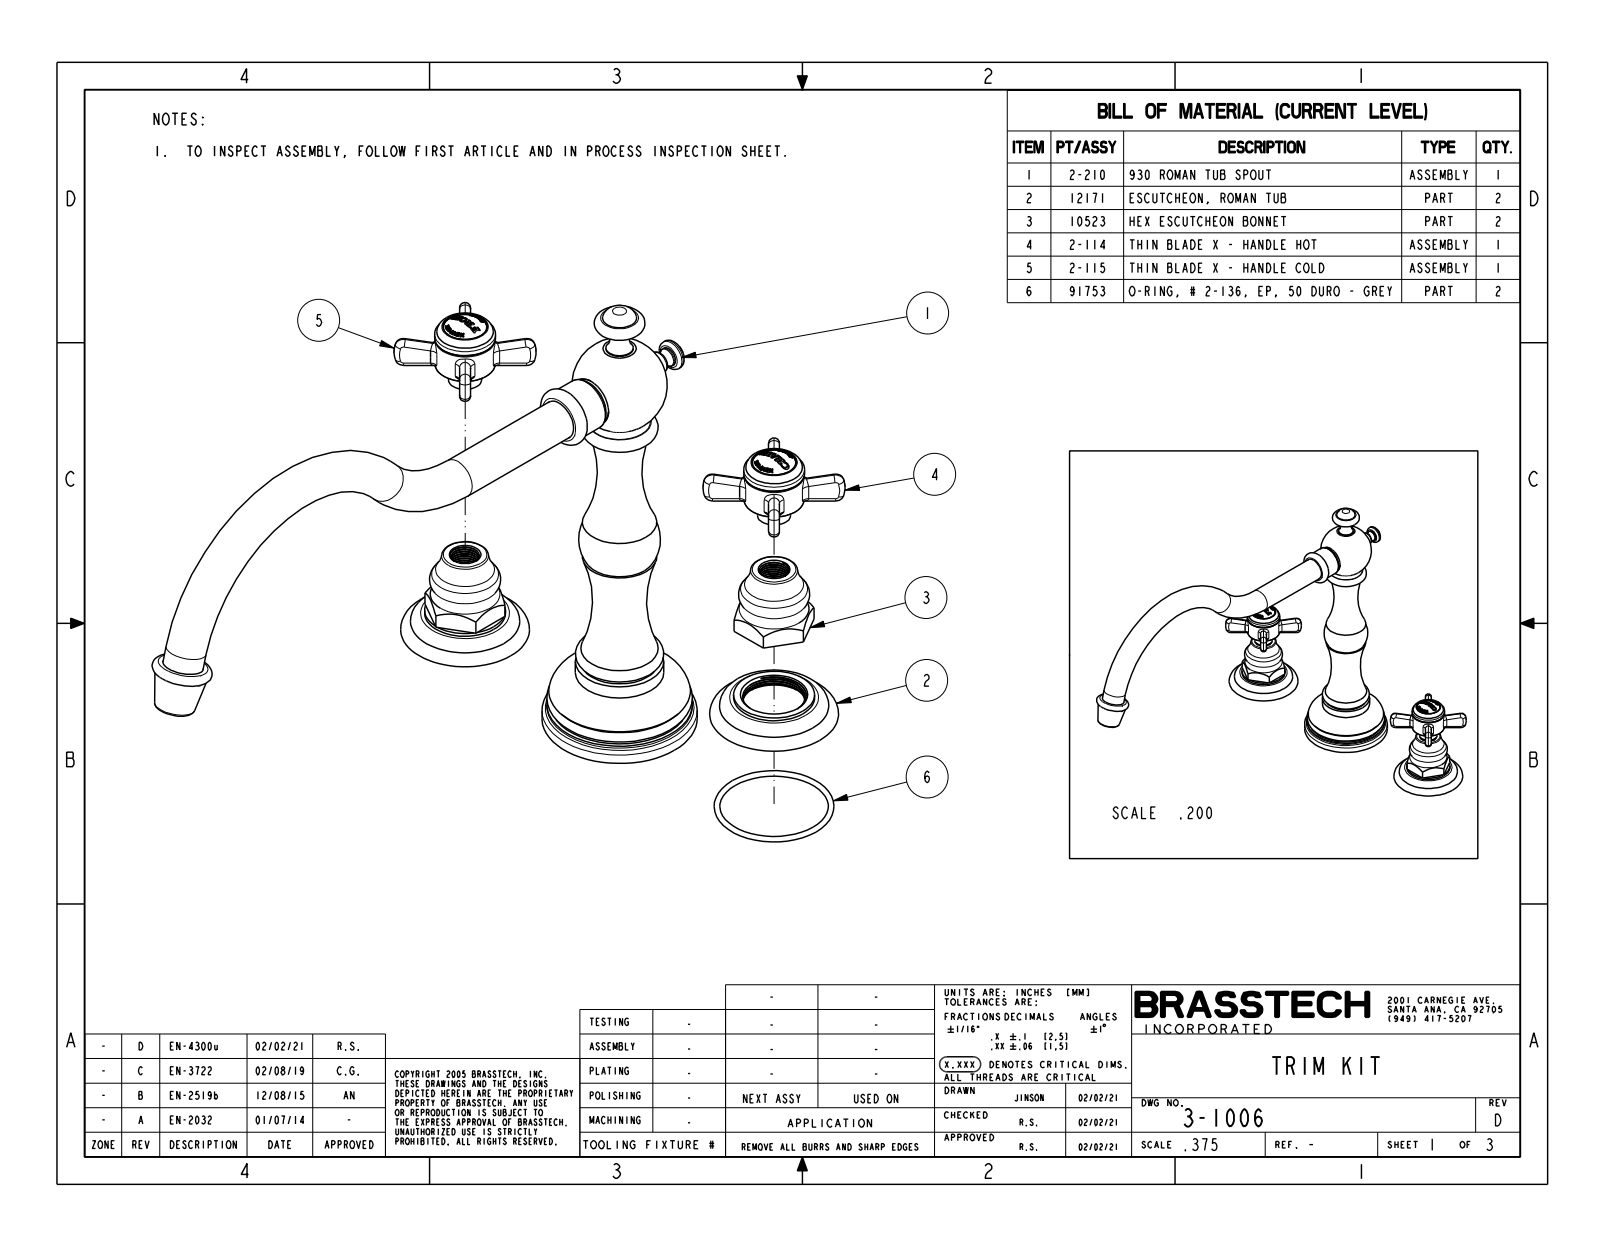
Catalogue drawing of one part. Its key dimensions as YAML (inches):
part_name: "3-1006"
step_written_by: "CREO PARAMETRIC BY PTC INC, 2018400 (CONFIG_CONTROL_DESIGN)"
units: inches
bodies: {solids: 3, faces: 1098, planar: 460, cylindrical: 334, other: 304}
overall_size: [13.395, 10.36, 9.745]
volume: 29.07
surface_area: 133.9
round_holes:
  - {diameter: 0.815, count: 2}
round_bosses_or_shafts:
  - {diameter: 0.99, count: 3}
  - {diameter: 1.482, count: 2}
  - {diameter: 1.115, count: 2}
  - {diameter: 1.1, count: 2}
  - {diameter: 0.75, count: 2}
  - {diameter: 0.603, count: 2}
  - {diameter: 0.4, count: 2}
  - {diameter: 2.84, count: 1}
partial_cylinders:
  - {radius: 0.011, count: 28}
  - {radius: 0.1, count: 25}
  - {radius: 0.025, count: 17}
  - {radius: 0.006, count: 14}
  - {radius: 0.005, count: 10}
  - {radius: 0.015, count: 10}
  - {radius: 0.006, count: 8}
  - {radius: 0.014, count: 8}
face_to_face_distances: [0.2, 5.656, 2.068, 1.687, 0.381, 5.456, 5.856, 1.693, 0.375, 1.312]
hole_center_spacings: [8]
